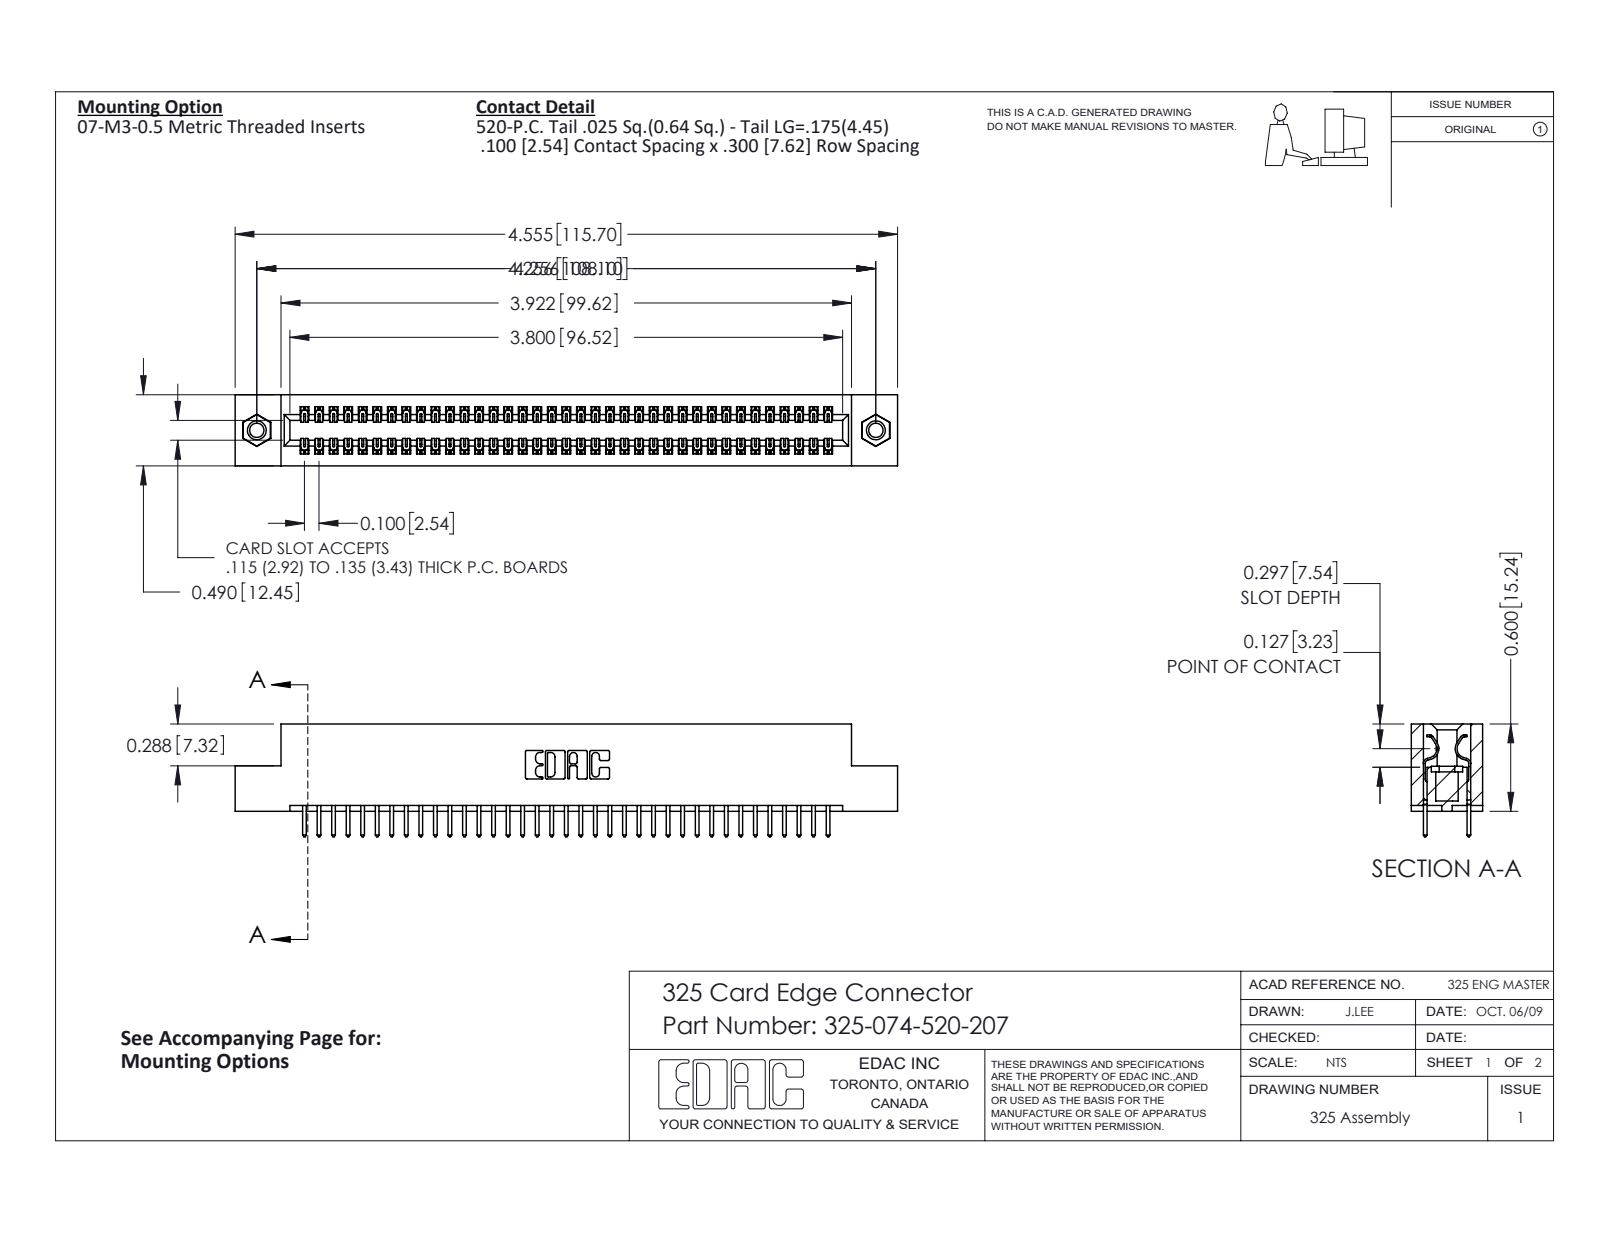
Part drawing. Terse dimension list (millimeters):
name: 325-292-001_325-293-120; 325 Part_TI; 325-074-520-207; 345-250-001_345-250-005-103
written by: SolidWorks 2016 (CONFIG_CONTROL_DESIGN)
unit: mm
bodies: 77 solids, 4022 faces (2766 planar, 1240 cylindrical, 16 other)
size: 115.7 × 19.7 × 12.4
volume: 14 900 mm³; area: 17 750 mm²
holes: 2× ⌀2.5, 2× ⌀3.2, 2× ⌀4.1
bosses: 2× ⌀3.9
rounds: 111× R0.2, 74× R0.3, 22× R0.3, 6× R0.2, 6× R0.8, 3× R0.7, 2× R0.4, 2× R0.6
face distances: 2.1, 10.3, 12.4, 7.6, 2.7, 9.7, 0.6, 8.3, 7, 14.2
hole spacings: 108.1
